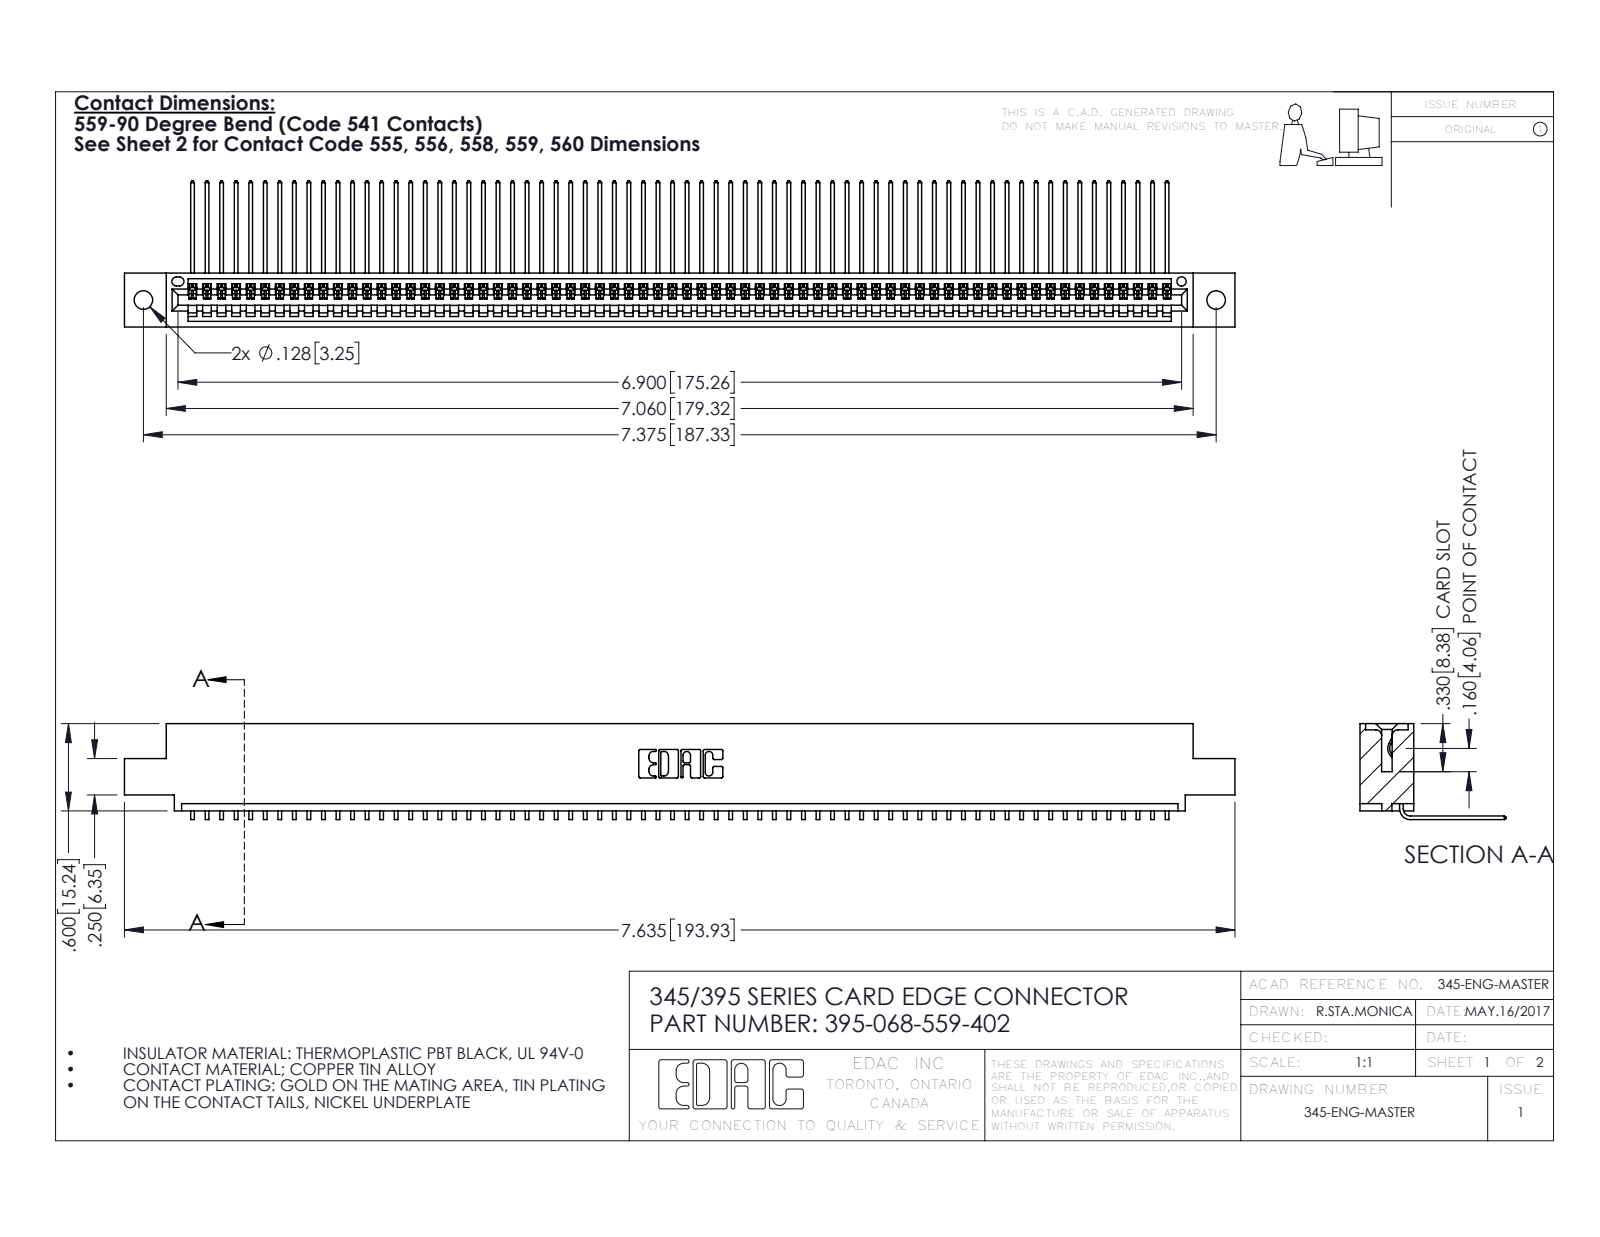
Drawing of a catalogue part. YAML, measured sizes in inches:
part_name: "395-068-559-402; 345-292-001_558 559 Tail - 1; 345 Part_0.110 Offset - 0.128 Dia"
step_written_by: "SolidWorks 2016 (CONFIG_CONTROL_DESIGN)"
units: inches
bodies: {solids: 69, faces: 4210, planar: 2940, cylindrical: 1270, other: 0}
overall_size: [7.635, 1.005, 0.659]
volume: 1.144
surface_area: 40.94
round_holes:
  - {diameter: 0.128, count: 2}
  - {diameter: 0.064, count: 1}
partial_cylinders:
  - {radius: 0.006, count: 136}
  - {radius: 0.01, count: 22}
  - {radius: 0.007, count: 6}
  - {radius: 0.031, count: 6}
  - {radius: 0.026, count: 3}
  - {radius: 0.031, count: 2}
  - {radius: 0.04, count: 2}
  - {radius: 0.014, count: 1}
face_to_face_distances: [0.072, 0.298, 0.37, 0.2, 0.098, 0.272, 0.025, 0.225, 0.149, 0.072]
hole_center_spacings: [0.27, 7.139, 7.375]
